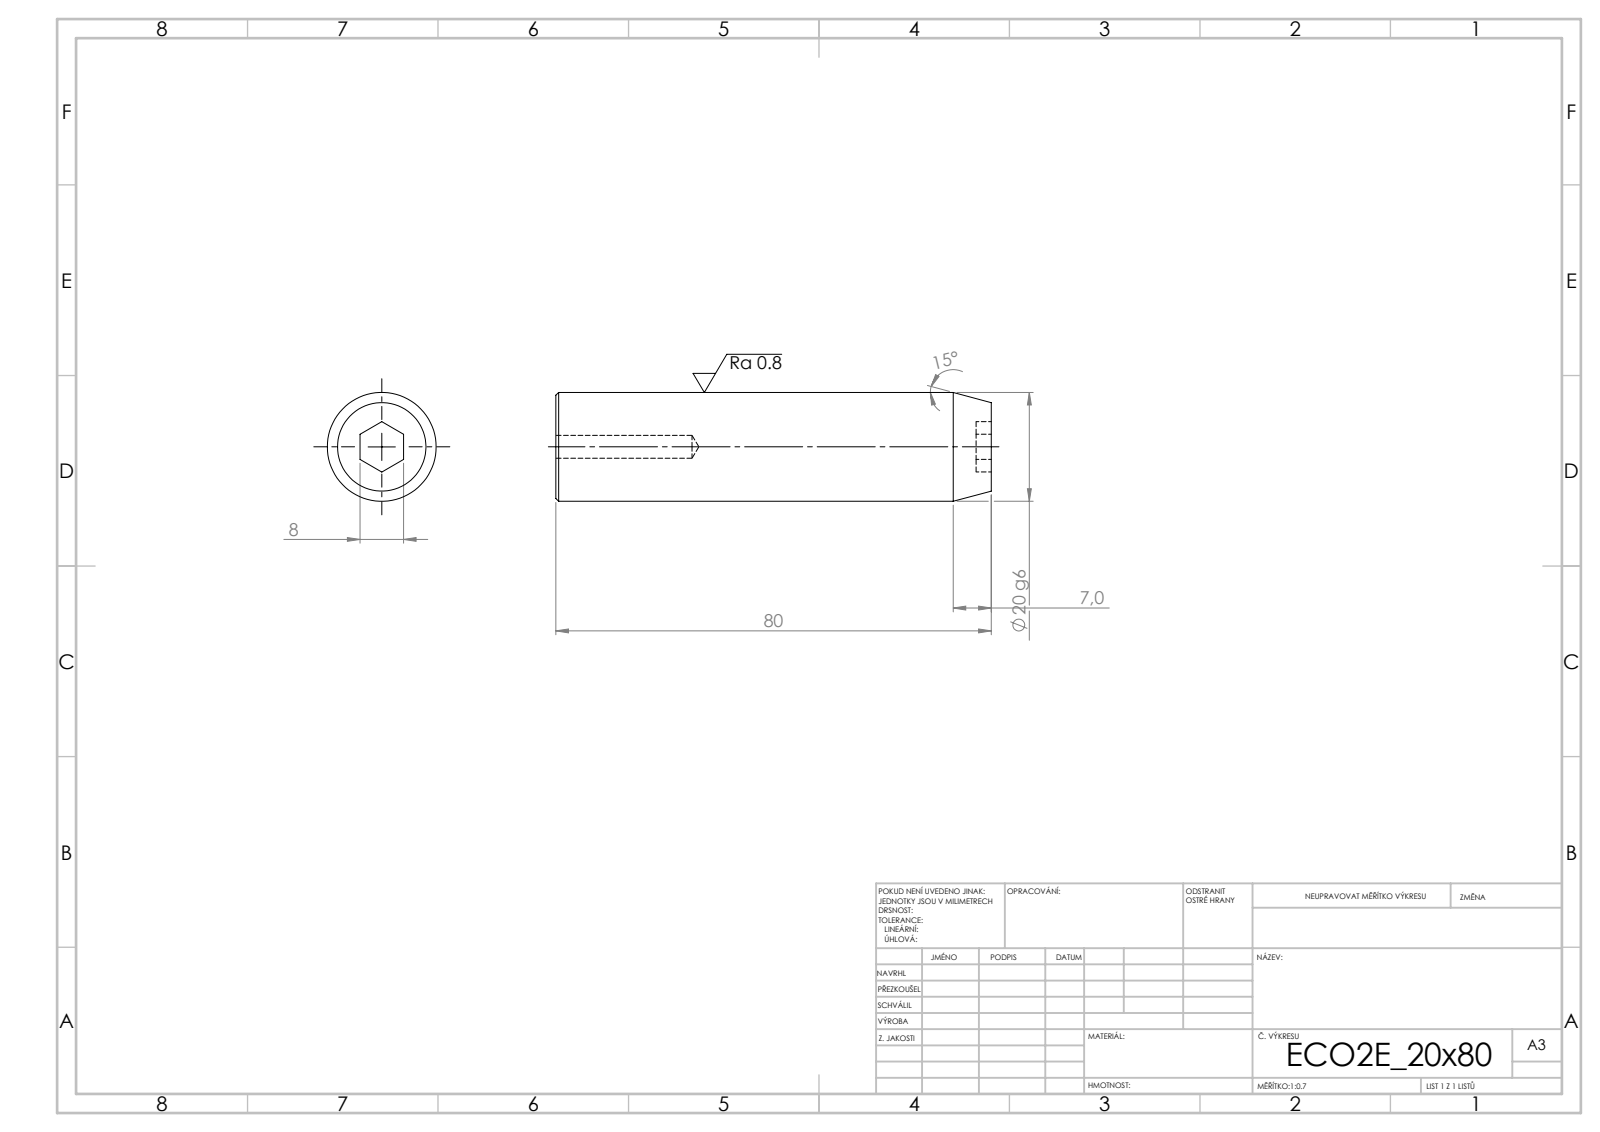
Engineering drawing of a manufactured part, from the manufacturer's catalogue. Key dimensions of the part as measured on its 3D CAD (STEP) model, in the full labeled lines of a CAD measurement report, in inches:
STEP written by: SolidWorks 2019 (CONFIG_CONTROL_DESIGN)
Units: inches
Bodies: 1 solid, 19 faces (9 planar, 4 cylindrical, 6 other)
Overall size (bounding box): 3.15 × 0.787 × 0.787
Volume: 1.479 in³ · Surface area: 9.164 in²
Round holes (diameter × count): ⌀0.165 ×1
Round bosses / shafts (diameter × count): ⌀0.787 ×1
Main face-to-face distances: 3.15, 0.11, 3.039, 0.315
